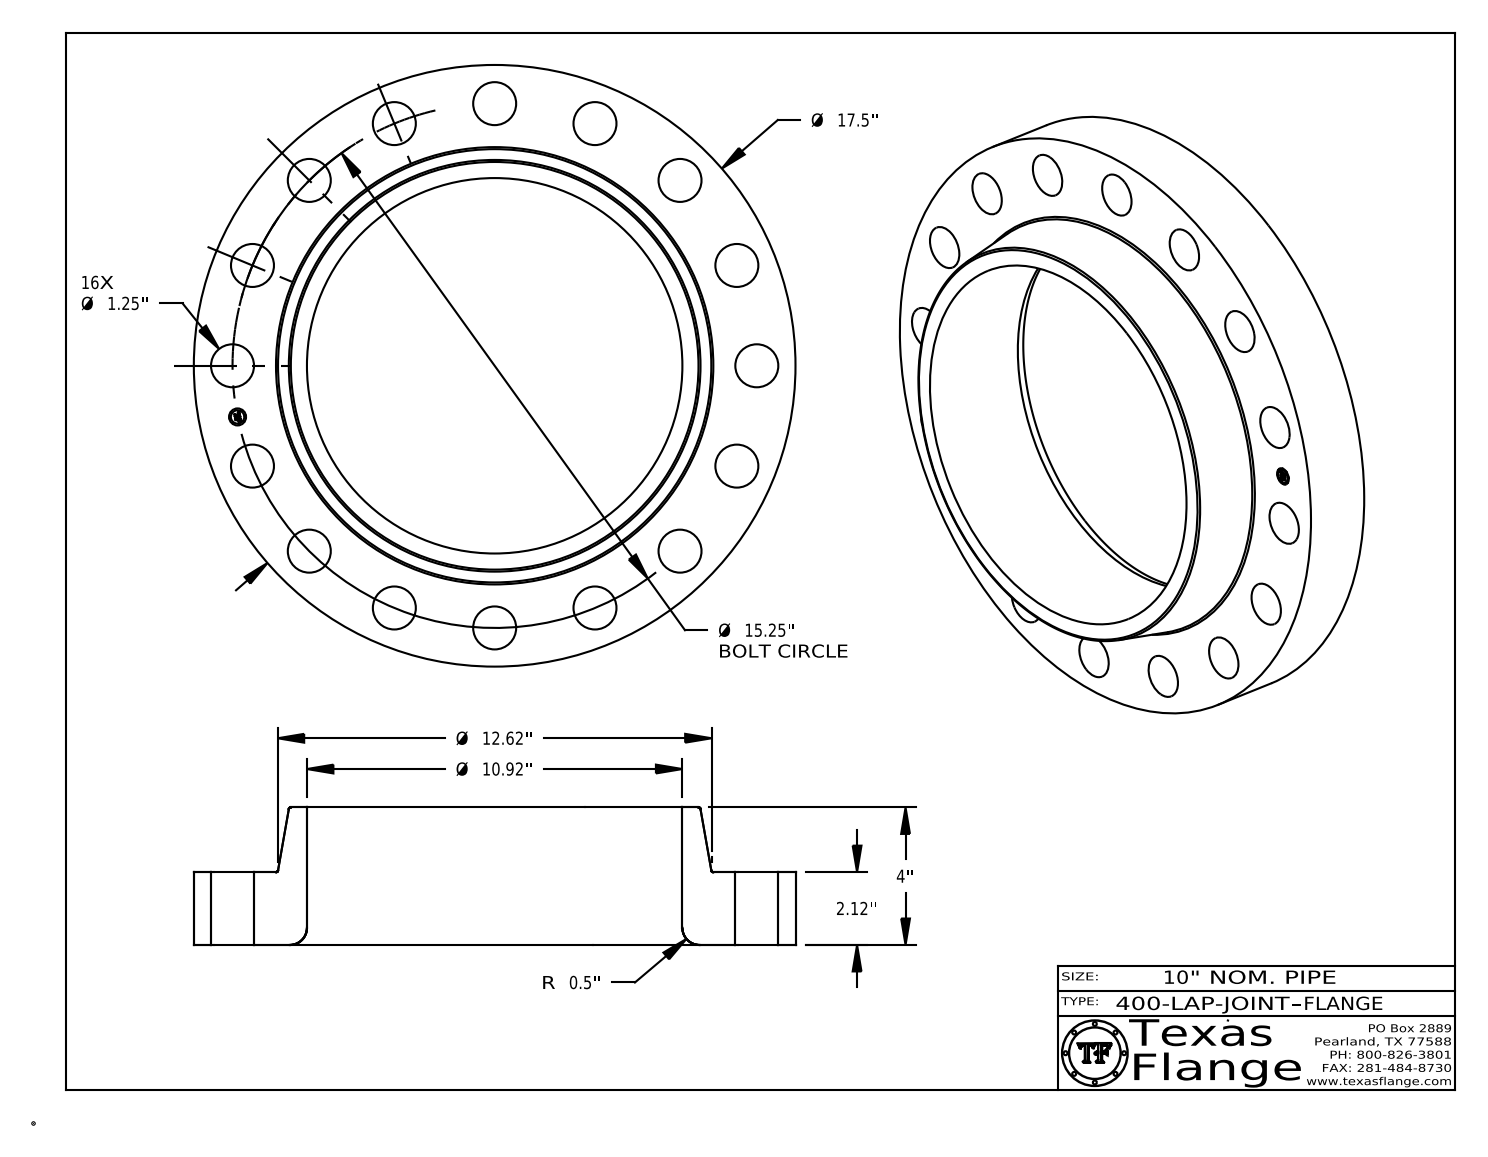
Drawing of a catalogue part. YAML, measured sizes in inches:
part_name: "400-LAP-JOINT FLANGE"
step_written_by: "CATIA V5 STEP AP214 (AUTOMOTIVE_DESIGN)"
units: inches
bodies: {solids: 1, faces: 432, planar: 368, cylindrical: 56, other: 8}
overall_size: [17.5, 17.5, 4]
volume: 314.8
surface_area: 693.9
round_holes:
  - {diameter: 1.25, count: 16}
  - {diameter: 0.495, count: 1}
  - {diameter: 10.92, count: 1}
round_bosses_or_shafts:
  - {diameter: 0.03, count: 8}
  - {diameter: 17.5, count: 1}
  - {diameter: 0.39, count: 1}
face_to_face_distances: [2.12, 4, 1.88, 0.015, 2.105, 1.895, 0.148, 0.145, 0.027, 0.096]
hole_center_spacings: [8.472, 10.783, 14.957, 14.089, 7.625, 2.975, 2.975, 5.836]
